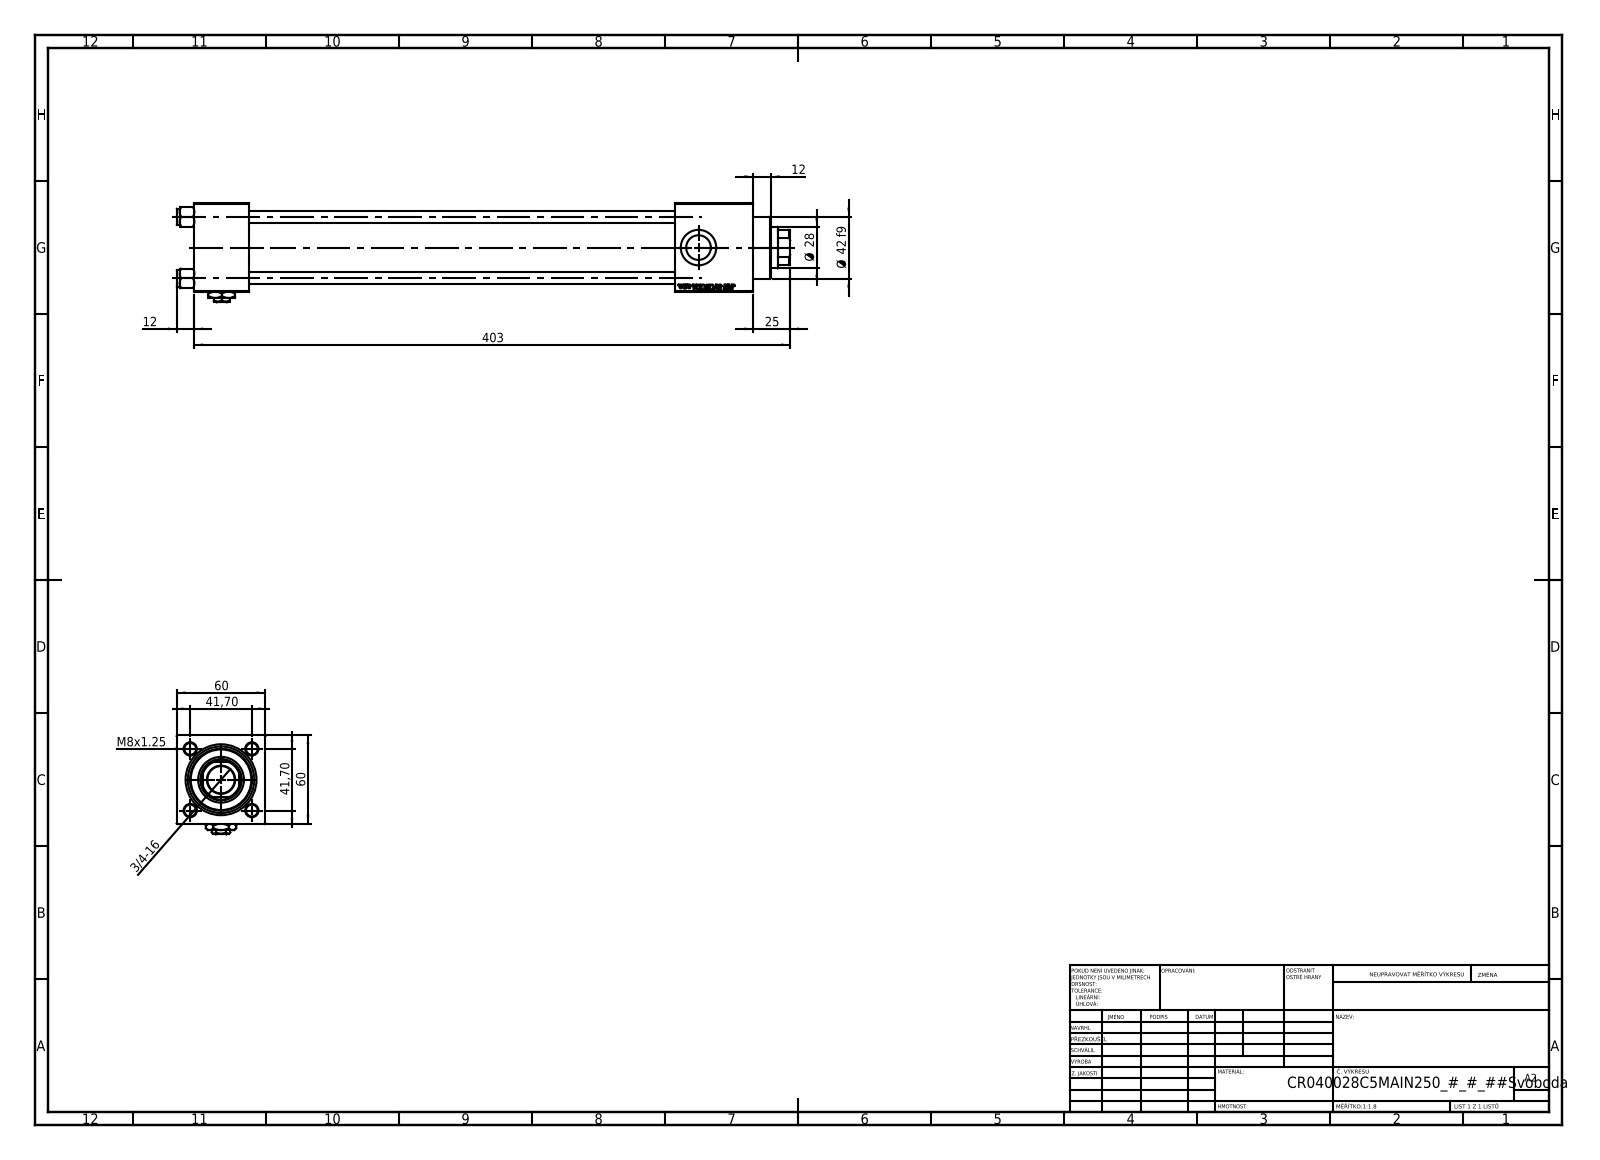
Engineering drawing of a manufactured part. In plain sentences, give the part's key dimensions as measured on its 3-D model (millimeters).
The part is named "NUT_M5_C; V215_VC_A; V215CR_C_TYCINKA; V215CR_C_Body (+2 more)". Its 3-D file was written by "SolidWorks 2019 (CONFIG_CONTROL_DESIGN)". It is 12 solids with 1202 faces: 550 planar, 94 cylindrical and 558 other. Overall it measures 415 by 67 by 60 millimeters. Its volume is 703 425 cubic millimeters and its surface area 218 666 square millimeters. Round holes: 4 of diameter 8, 2 of diameter 7, 2 of diameter 16.66, 2 of diameter 24, 1 of diameter 18.5, 1 of diameter 28, 1 of diameter 31, 1 of diameter 40, 1 of diameter 45. Round bosses or shafts: 4 of diameter 11, 1 of diameter 46, 1 of diameter 42. Partial cylindrical surfaces (rounded edges, fillets, slot ends): 1 of radius 13.5. The main face-to-face distances are 60, 37, 325, 288, 349.3, 312.3, 24.3, 53, 378, 341. The hole center spacings are 29.49, 41.7, 58.97.
